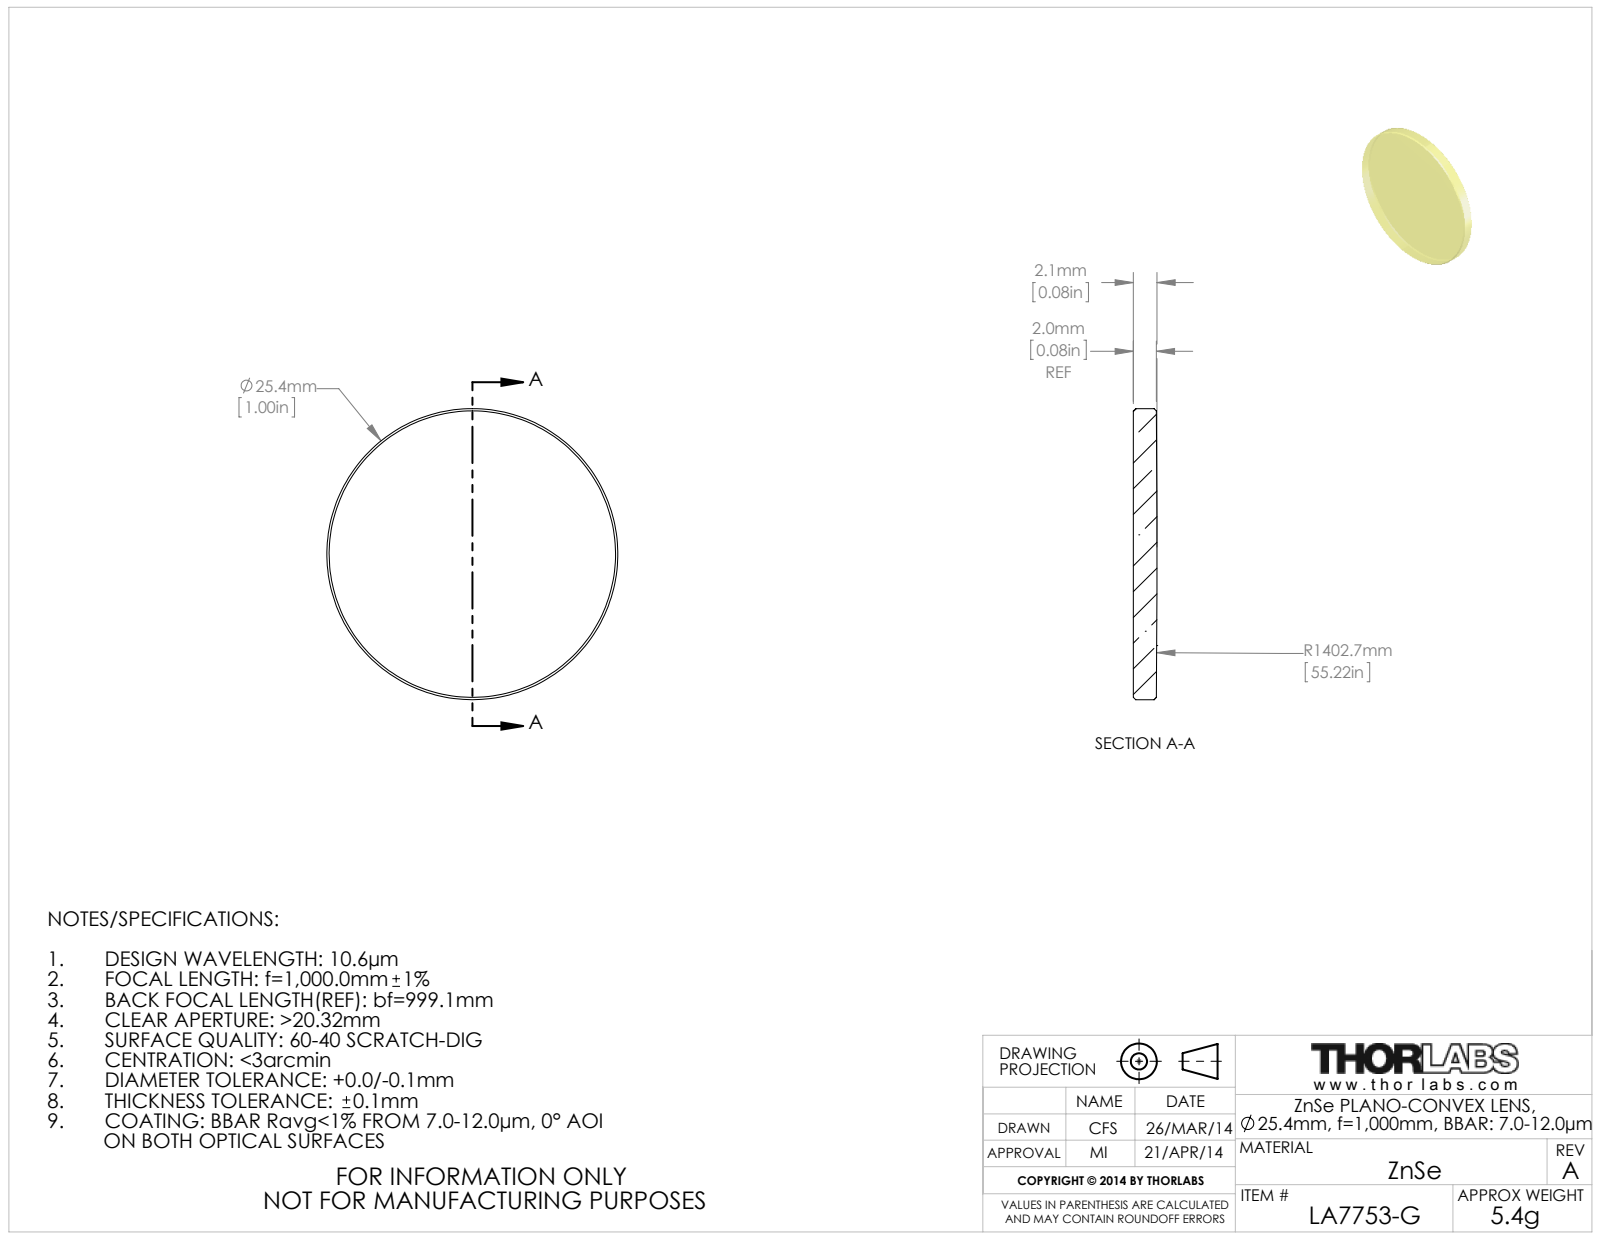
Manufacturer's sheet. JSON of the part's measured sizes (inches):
{"part_name": "TTN023920-E0W", "step_written_by": "SolidWorks 2012 (CONFIG_CONTROL_DESIGN)", "units": "inches", "bodies": {"solids": 1, "faces": 9, "planar": 1, "cylindrical": 2, "other": 6}, "overall_size": [1, 1, 0.081], "volume_in3": 0.063, "surface_area_in2": 1.79, "round_bosses_or_shafts": [[1, 1]]}
